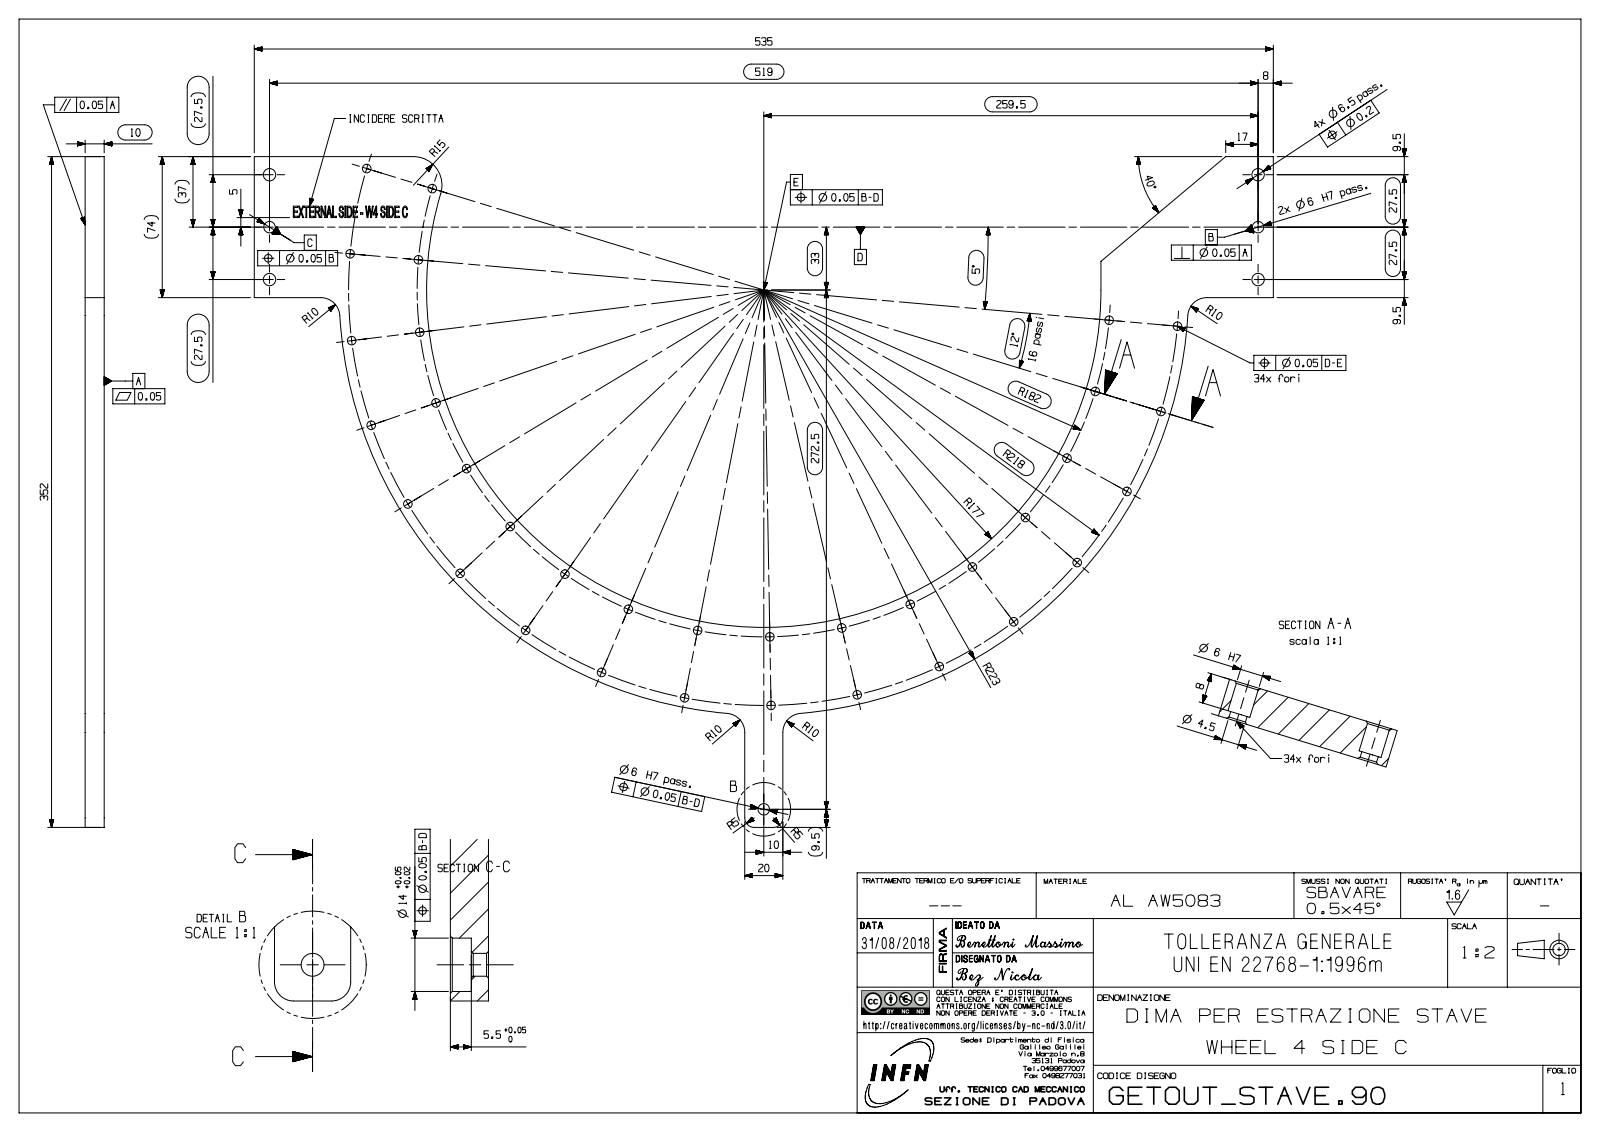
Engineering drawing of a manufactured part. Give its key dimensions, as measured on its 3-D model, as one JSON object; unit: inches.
{"part_name": "bezA730AE56cd3n", "step_written_by": "SIEMENS PLM Software NX 12.0 (AUTOMOTIVE_DESIGN)", "units": "inches", "bodies": {"solids": 1, "faces": 415, "planar": 214, "cylindrical": 86, "other": 115}, "overall_size": [21.063, 13.858, 0.394], "volume_in3": 24.66, "surface_area_in2": 167.2, "round_holes": [[0.236, 37], [0.177, 34], [0.256, 4], [0.551, 1]], "partial_cylinders_radius": [[0.394, 4], [0.197, 2], [0.591, 1], [6.969, 1], [8.78, 1]], "face_to_face_distances": [0.394, 10.138, 10.925, 21.063, 2.913, 0.787, 0.079, 0.315, 17.5, 7.362], "hole_center_spacings": [5.05, 2.167, 3.556, 6.535, 7.969, 2.167, 9.327, 10.59]}
